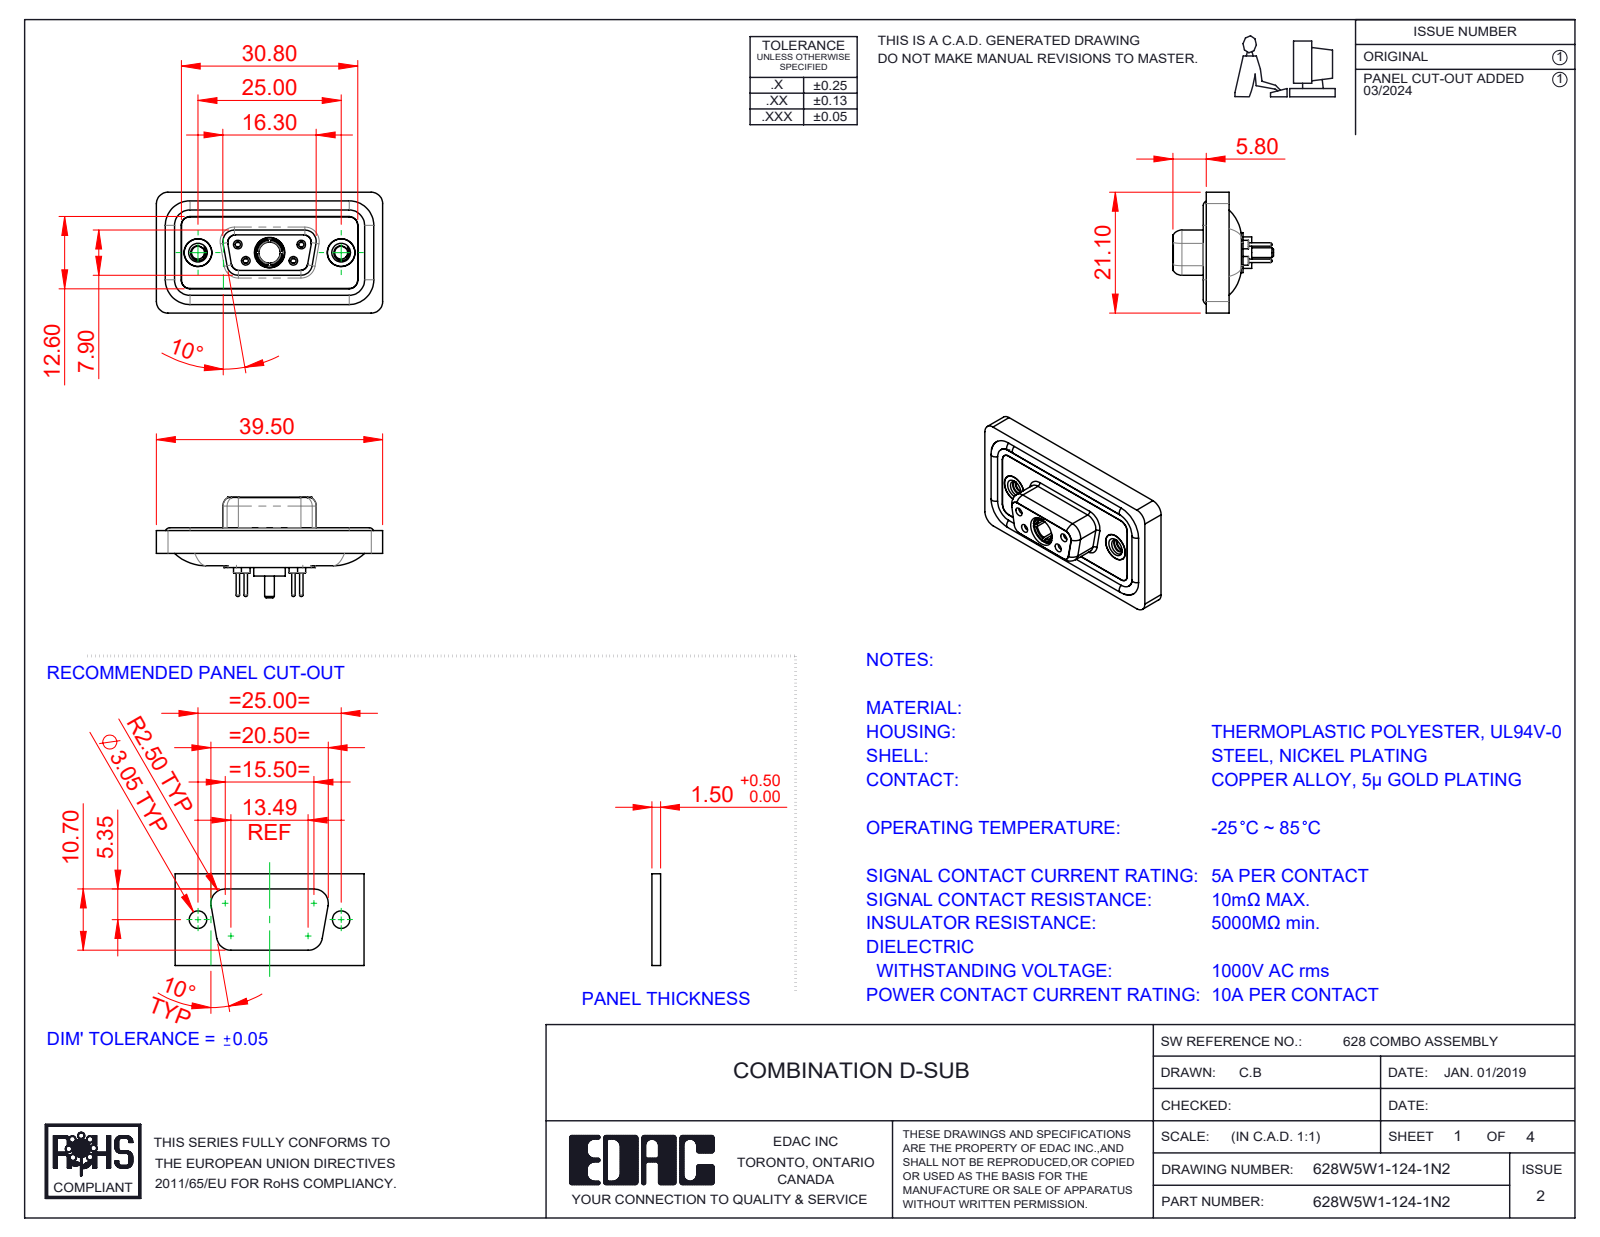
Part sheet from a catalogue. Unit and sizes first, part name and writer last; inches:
Units: inches
Overall size (bounding box): 1.555 × 0.831 × 0.691
Round holes (diameter × count): ⌀0.035 ×4, ⌀0.043 ×4, ⌀0.059 ×4, ⌀0.079 ×4, ⌀0.191 ×3, ⌀0.063 ×2, ⌀0.067 ×2, ⌀0.089 ×2, ⌀0.157 ×2, ⌀0.159 ×2, ⌀0.197 ×2, ⌀0.146 ×1
Round bosses / shafts (diameter × count): ⌀0.063 ×6, ⌀0.087 ×4, ⌀0.024 ×4, ⌀0.195 ×2, ⌀0.189 ×2, ⌀0.217 ×1, ⌀0.205 ×1, ⌀0.195 ×1
Partial cylindrical surfaces — rounded edges, fillets, slot ends (radius × count): R0.059 ×22, R0.079 ×18, R0.053 ×8, R0.063 ×8, R0.01 ×4, R0.02 ×4, R0.024 ×4, R0.026 ×4
Main face-to-face distances: 0.016, 0.114, 0.071, 0.043, 0.063, 0.02, 0.222, 0.293, 0.211, 0.26
Hole centre spacings: 0.124, 0.225, 0.28, 0.492, 0.713, 0.173, 0.173, 0.327
Volume: 0.29 in³ · Surface area: 11.82 in²
Bodies: 13 solids, 680 faces (194 planar, 287 cylindrical, 199 other)
Part name (STEP PRODUCT): 628Combo Threaded Rivet_2; 628Combo Shell Rear_09 Contacts; Power Socket_10A S; 628Combo Contact Row 1_24 (+5 more)
STEP written by: SolidWorks 2023 (CONFIG_CONTROL_DESIGN)
